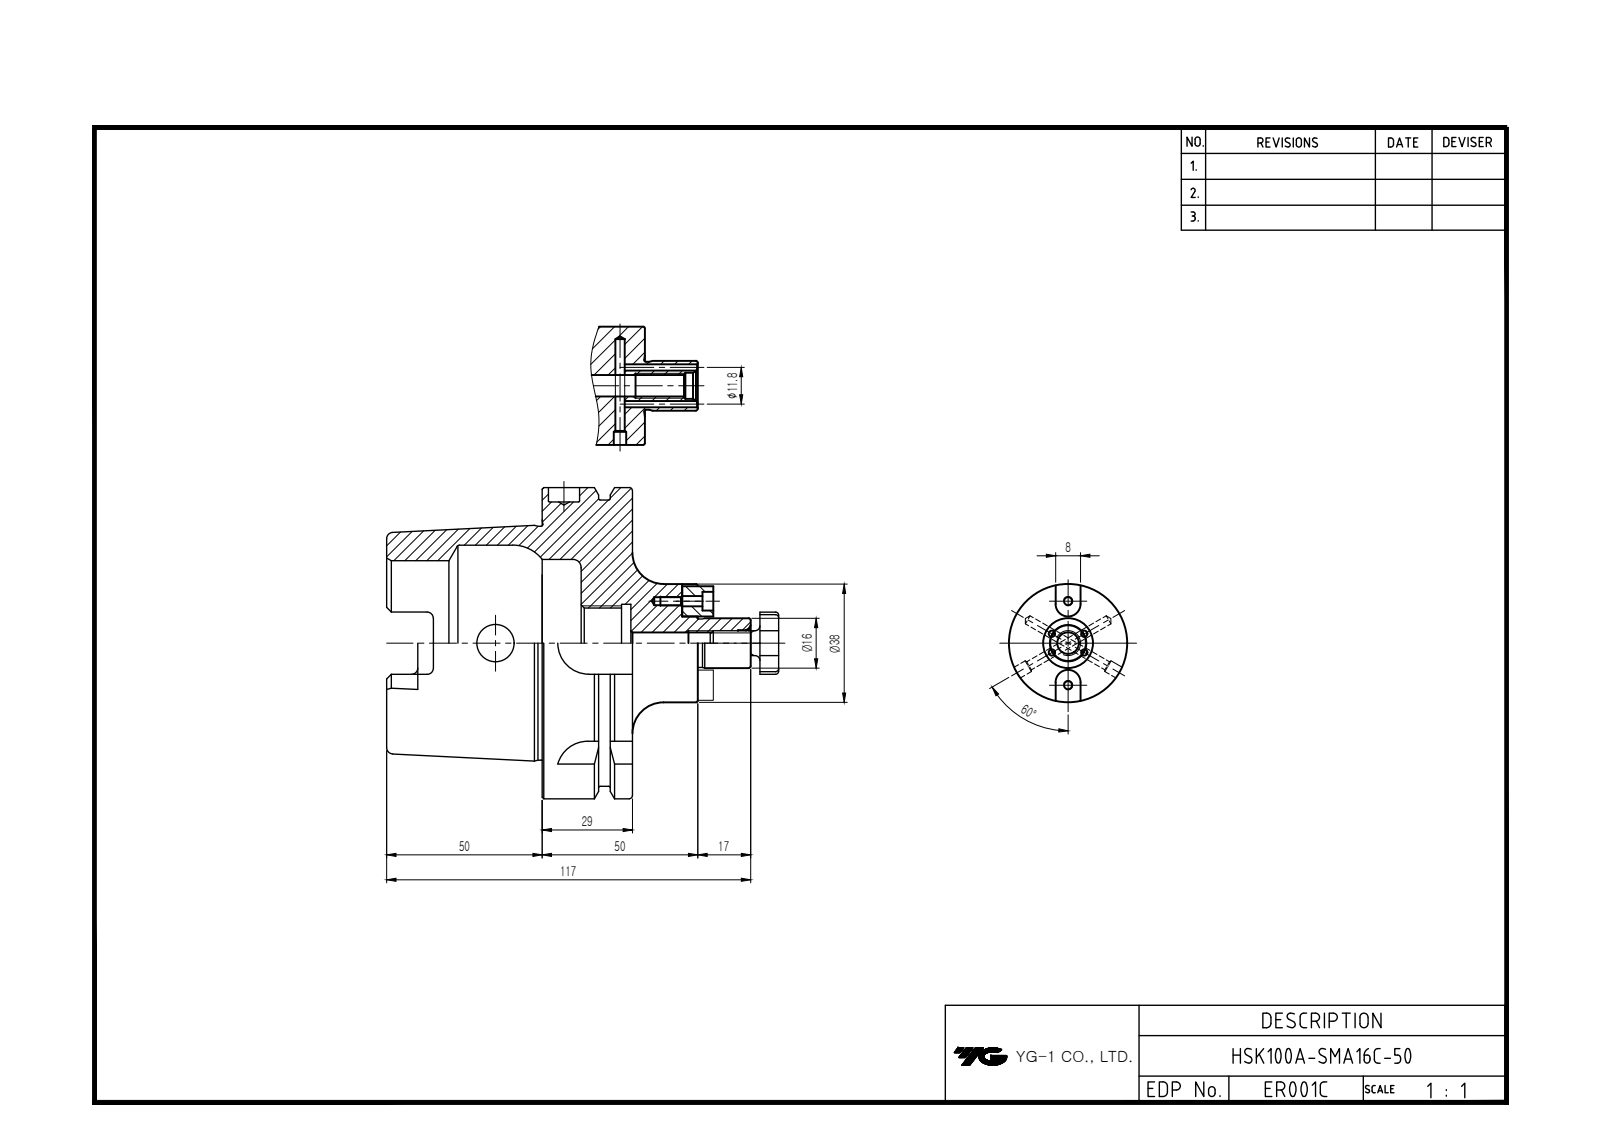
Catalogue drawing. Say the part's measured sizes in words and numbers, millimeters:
The part is named "LO-HSK100A-SMA16C-50; SMA16E-DRIVE KEY-SECO; HEX'' WRENCH BOLT-M3x0.5x12L; SMA16-M8x1.25x16L". Its 3-D file was written by "Autodesk Inventor 2025 (AP242_MANAGED_MODEL_BASED_3D_ENGINEERING_MIM_LF)". It is 6 solids with 205 faces: 85 planar, 61 cylindrical and 59 other. Overall it measures 128 by 100 by 100 millimeters. Its volume is 285 414 cubic millimeters and its surface area 57 159 square millimeters. Round holes: 4 of diameter 2, 2 of diameter 2.46, 2 of diameter 3.3, 2 of diameter 6, 1 of diameter 6.65, 1 of diameter 8.4, 1 of diameter 10, 1 of diameter 12, 1 of diameter 22.38, 1 of diameter 25, 1 of diameter 53, 1 of diameter 63. Round bosses or shafts: 2 of diameter 5.5, 2 of diameter 3, 1 of diameter 100, 1 of diameter 92, 1 of diameter 75.41, 1 of diameter 38, 1 of diameter 16, 1 of diameter 8. Partial cylindrical surfaces (rounded edges, fillets, slot ends): 10 of radius 2, 5 of radius 10, 4 of radius 4, 4 of radius 4.88. The main face-to-face distances are 29, 16.5, 12.5, 50, 62.5, 79, 21, 100, 37.5, 16. The hole center spacings are 5.9, 11.72, 17.23, 10.22, 11.8, 13.5, 27.
